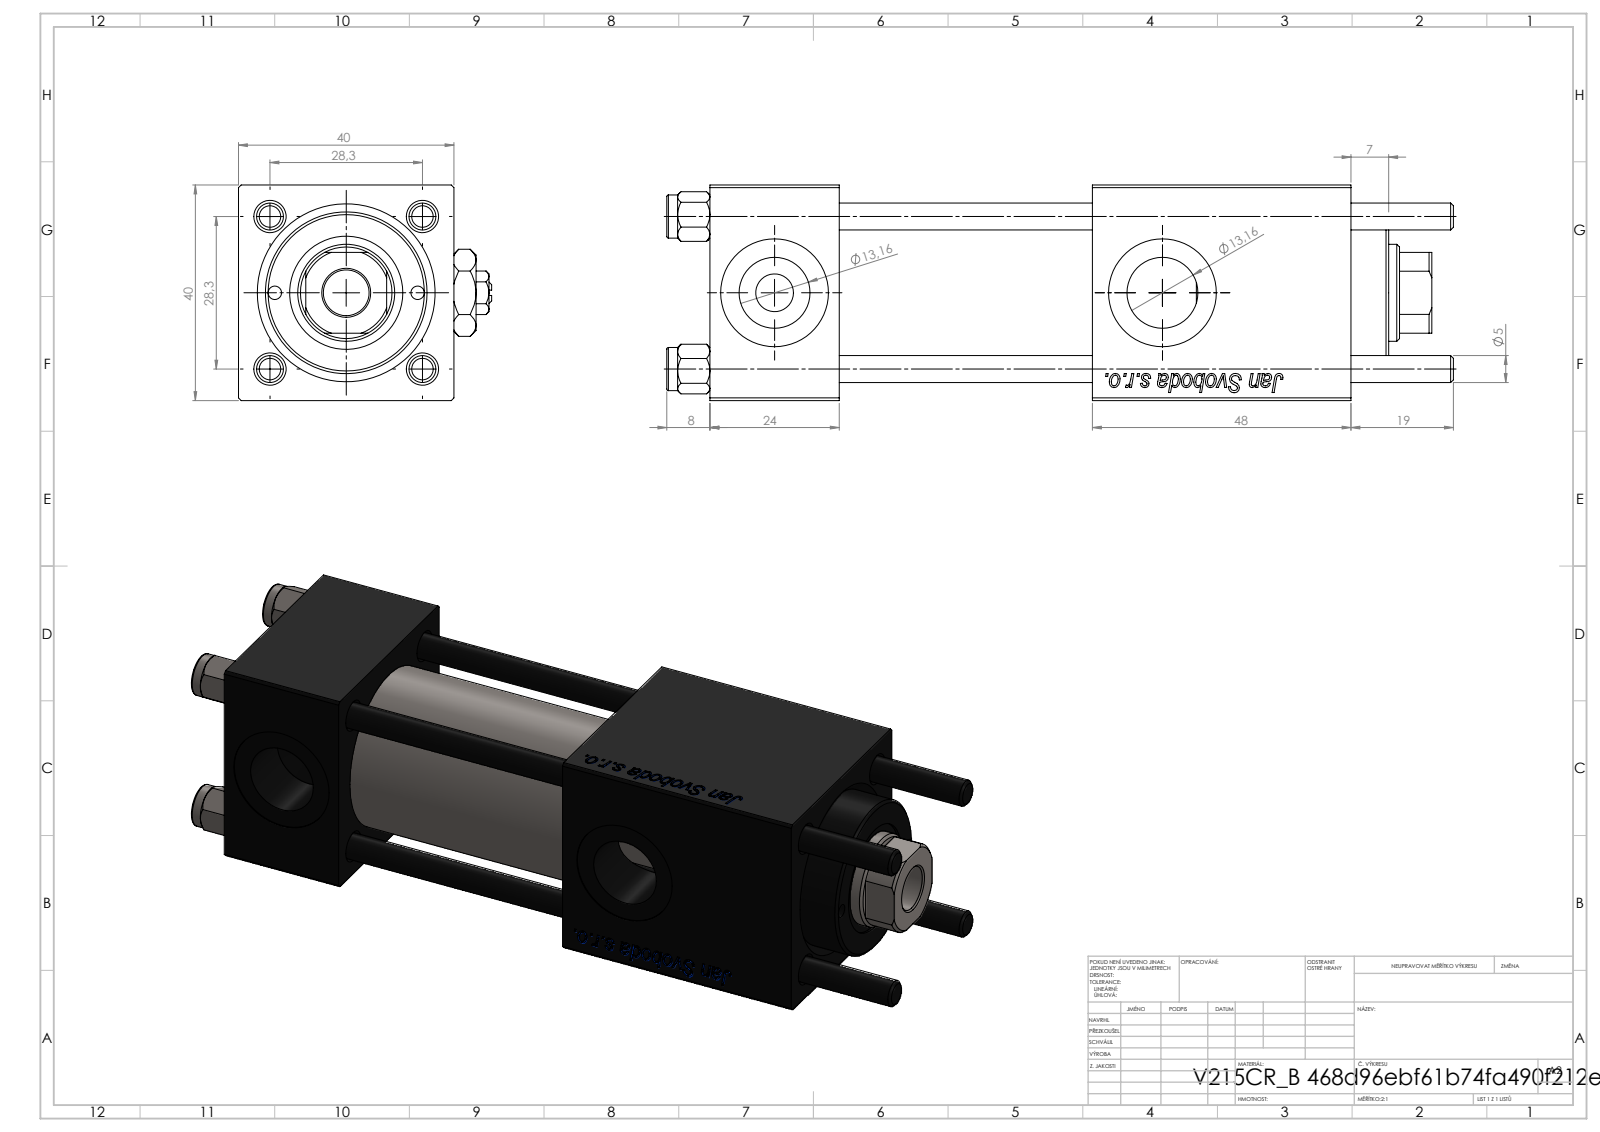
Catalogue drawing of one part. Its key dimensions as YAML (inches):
part_name: "NUT_M5_B; V215_VC_A; V215CR_B-1; Zatka_pro_OIL_PORT (+2 more)"
step_written_by: "SolidWorks 2019 (CONFIG_CONTROL_DESIGN)"
units: inches
bodies: {solids: 12, faces: 1206, planar: 454, cylindrical: 84, other: 668}
overall_size: [5.748, 1.85, 1.575]
volume: 9.259
surface_area: 95.83
round_holes:
  - {diameter: 0.197, count: 4}
  - {diameter: 0.787, count: 3}
  - {diameter: 0.098, count: 2}
  - {diameter: 0.276, count: 2}
  - {diameter: 0.518, count: 2}
  - {diameter: 0.335, count: 1}
  - {diameter: 0.709, count: 1}
  - {diameter: 0.827, count: 1}
  - {diameter: 0.984, count: 1}
  - {diameter: 1.181, count: 1}
round_bosses_or_shafts:
  - {diameter: 0.315, count: 4}
  - {diameter: 1.22, count: 1}
partial_cylinders:
  - {radius: 0.335, count: 1}
face_to_face_distances: [1.575, 0.945, 1.85, 2.795, 3.555, 2.61, 0.76, 1.567, 1.89, 4.685]
hole_center_spacings: [0.558, 0.788, 1.114, 1.214, 0.522, 1.576, 1.043, 2.835]
